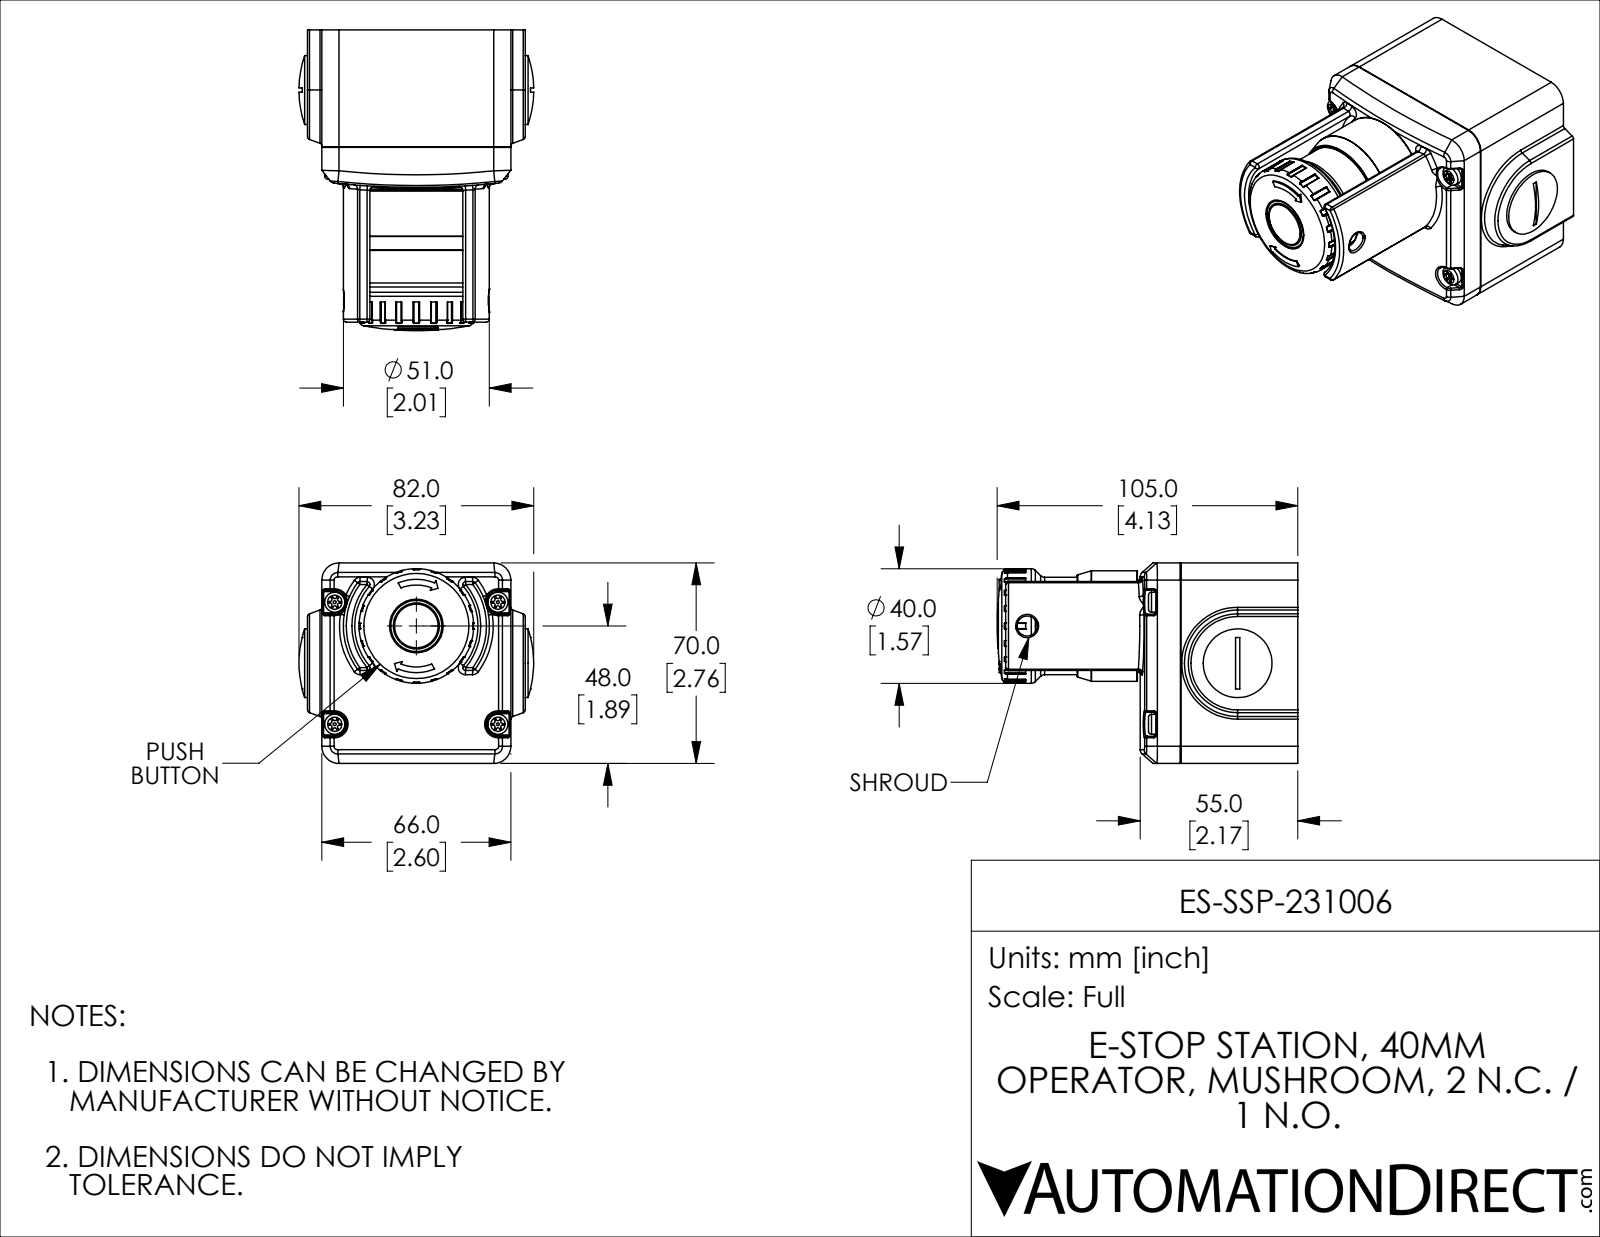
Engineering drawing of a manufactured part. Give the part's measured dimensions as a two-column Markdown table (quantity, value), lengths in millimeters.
| quantity | value |
| --- | --- |
| part name | ES-SSP-231006 |
| STEP written by | SolidWorks 2016 (AUTOMOTIVE_DESIGN) |
| units | millimeters |
| bodies | 10 solids, 751 faces (219 planar, 276 cylindrical, 256 other) |
| overall size | 105 × 81.98 × 70 |
| volume | 296 547 mm³ |
| surface area | 57 744 mm² |
| round holes (diameter × count) | 4.4 × 4, 7 × 1, 31.1 × 1, 37 × 1 |
| round bosses / shafts (diameter × count) | 7 × 4, 1 × 4, 40 × 1, 38.6 × 1, 34 × 1, 32 × 1, 24 × 1 |
| partial cylindrical surfaces (radius × count) | 0.1 × 80, 0.76 × 24, 1 × 18, 0.5 × 14, 0.2 × 4, 4.2 × 4, 6 × 4, 2 × 2 |
| main face-to-face distances | 41, 5, 71, 70, 56, 15, 76, 66, 56.8, 15.8 |
| hole center spacings | 31.38, 49.93, 54, 58, 79.25 |
